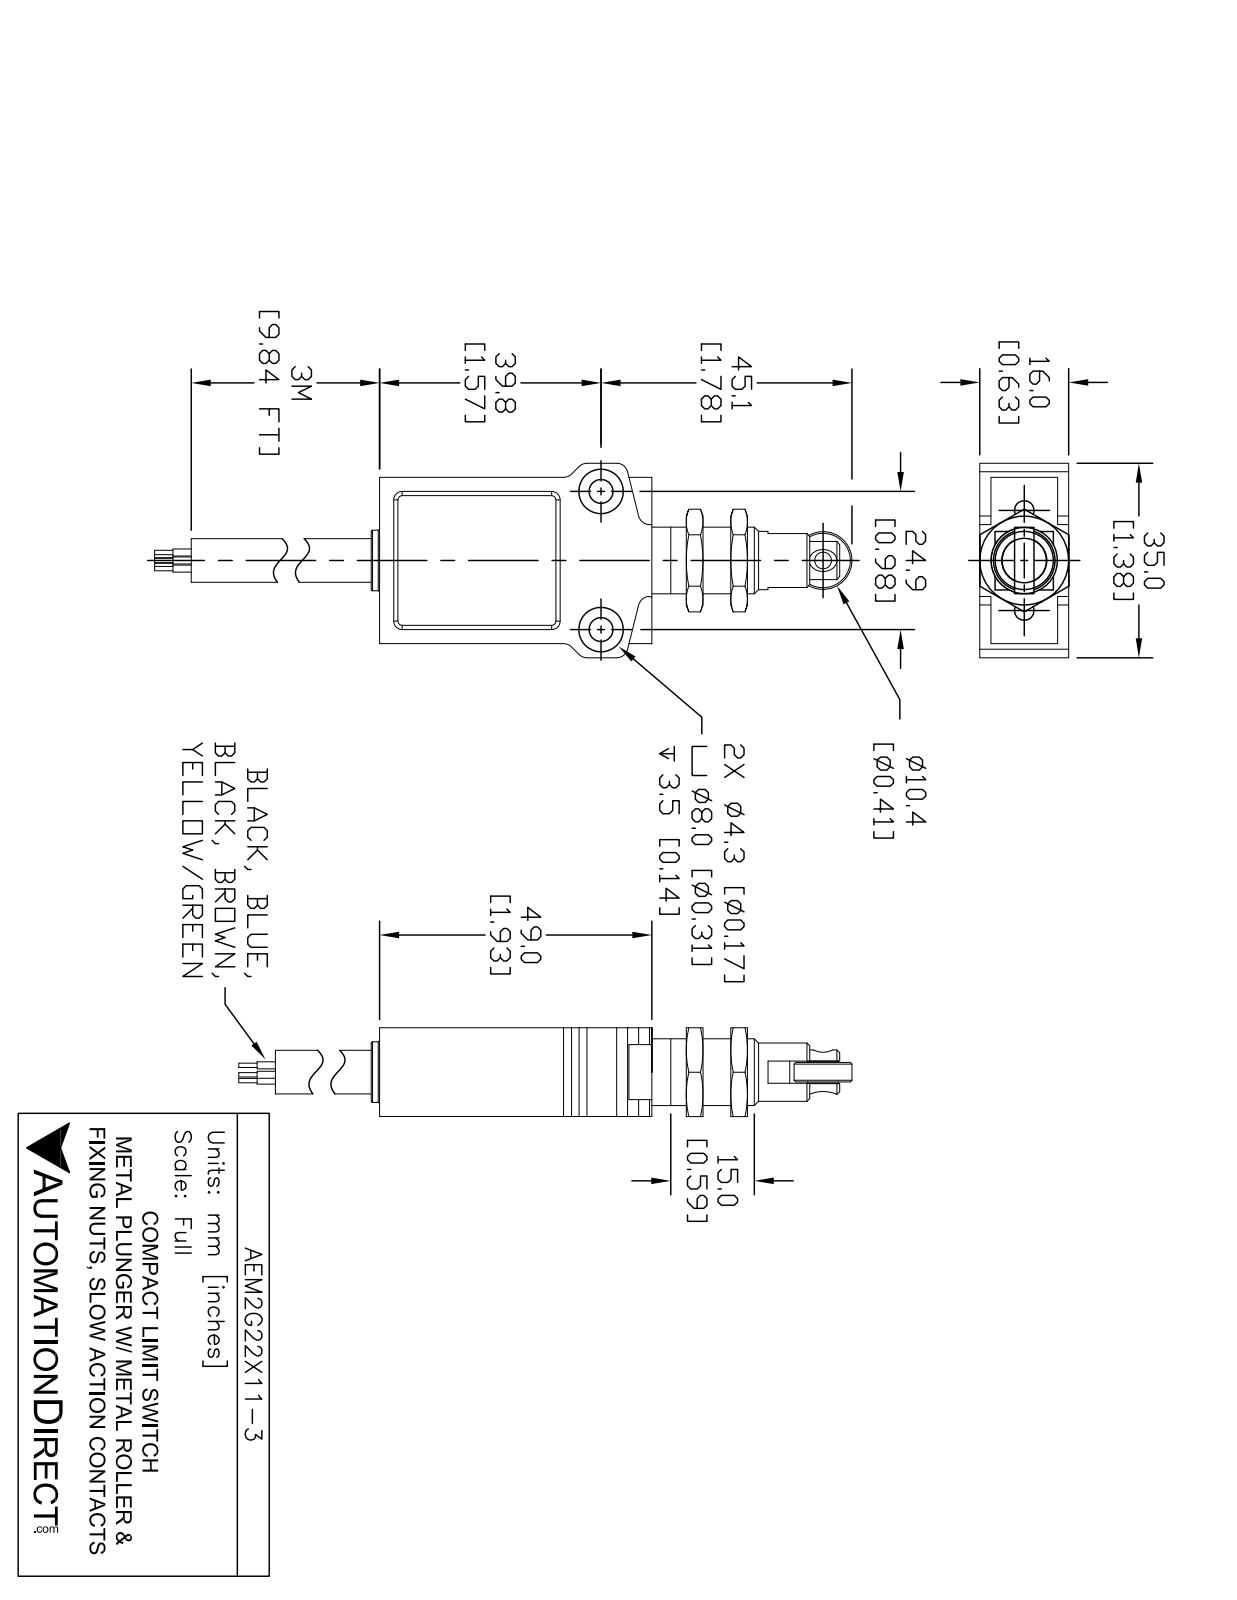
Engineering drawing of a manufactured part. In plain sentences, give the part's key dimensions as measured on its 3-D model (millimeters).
The part is named "AEM2G22X11-3_Default". Its 3-D file was written by "SolidWorks 2021 (CONFIG_CONTROL_DESIGN)". It is 2 solids with 191 faces: 98 planar, 47 cylindrical and 46 other. Overall it measures 100.7 by 35.1 by 16 millimeters. Its volume is 25 650 cubic millimeters and its surface area 9 052 square millimeters. Round holes: 2 of diameter 4.5, 2 of diameter 8.7. Round bosses or shafts: 5 of diameter 1.3, 5 of diameter 0.8, 2 of diameter 10.4, 1 of diameter 11.9, 1 of diameter 10.9, 1 of diameter 7.9. Partial cylindrical surfaces (rounded edges, fillets, slot ends): 8 of radius 0.8, 8 of radius 2, 1 of radius 3.4. The main face-to-face distances are 0.8, 15.2, 14.5, 16, 30, 3, 7.6, 49, 4.7, 11.3. The hole center spacings are 24.9.
